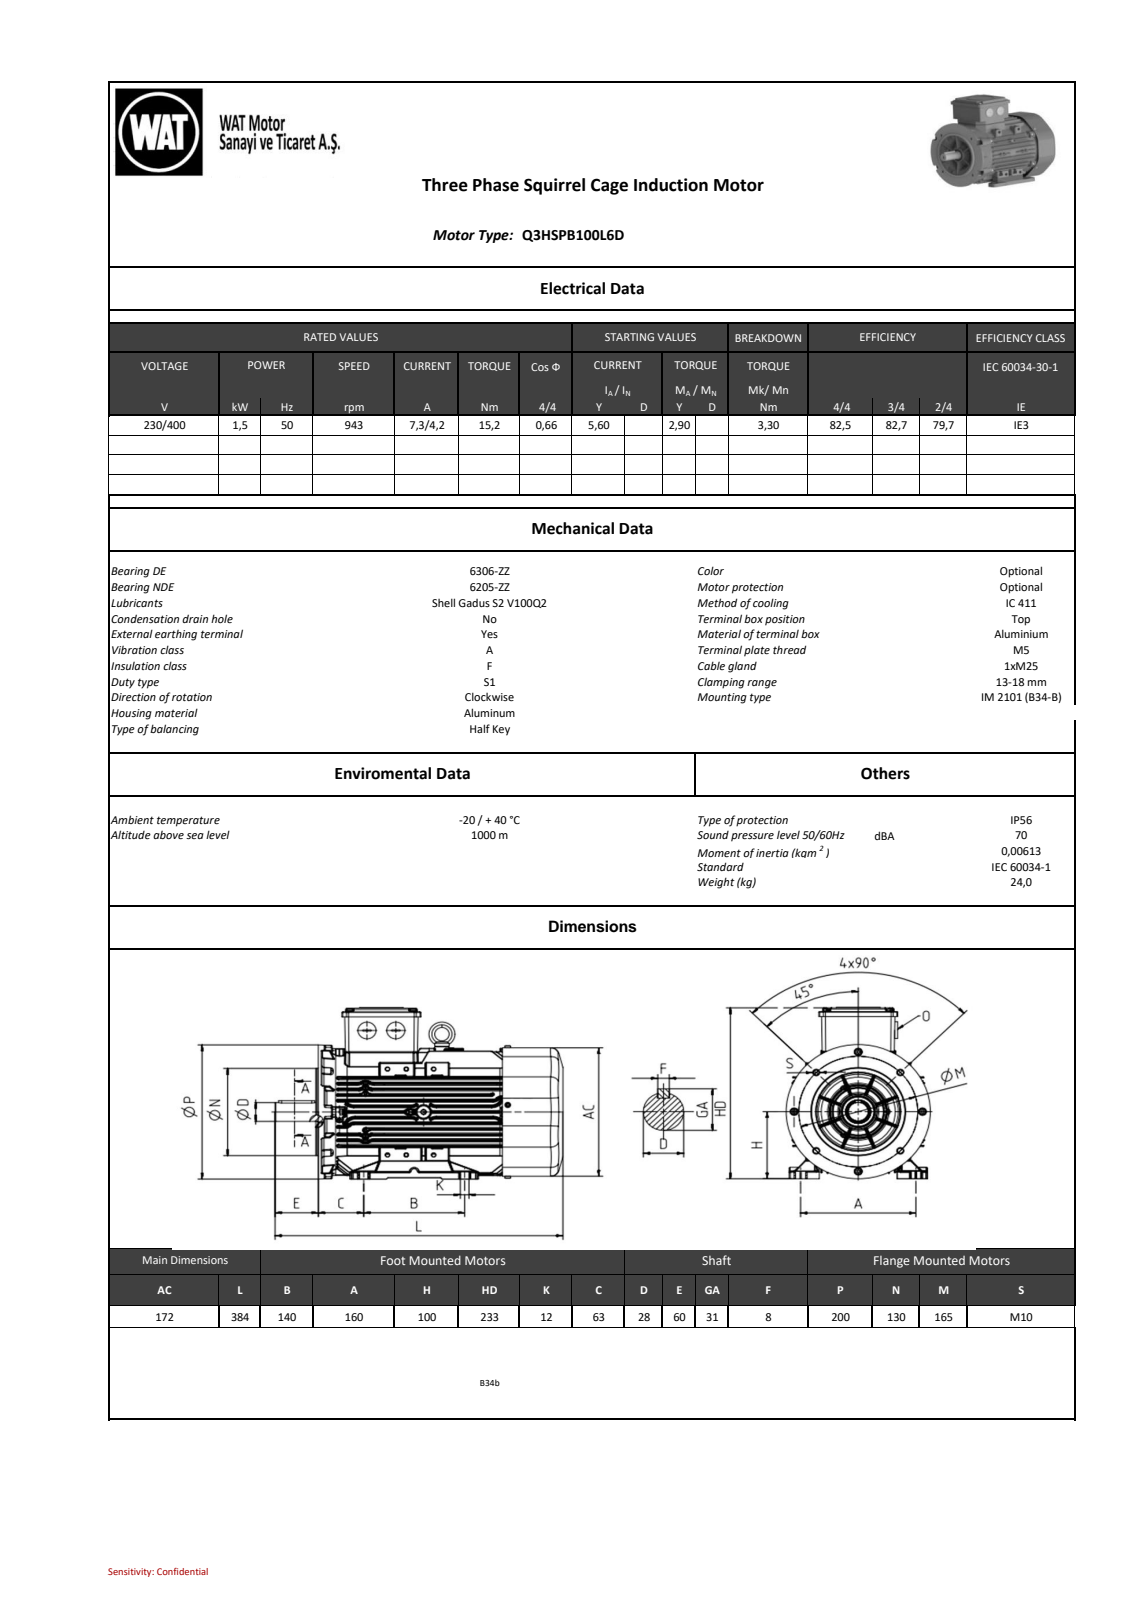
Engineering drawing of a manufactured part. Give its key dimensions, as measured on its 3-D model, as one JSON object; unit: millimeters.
{"part_name": "QHS Series_ 100_B34b DEEP COVER_stp_objects", "step_written_by": "SIEMENS PLM Software NX2206.8101 (AUTOMOTIVE_DESIGN)", "units": "millimeters", "bodies": {"solids": 0, "faces": 7543, "planar": 1878, "cylindrical": 3298, "other": 2367}, "overall_size": [384.19, 233.22, 200.35], "round_holes": [[9, 4], [3.5, 3], [8.5, 1], [9.87, 1], [10.5, 1], [79.79, 1], [97.79, 1], [115.78, 1]], "round_bosses_or_shafts": [[8, 7], [5, 5], [10, 4], [9.5, 4], [25, 2], [130, 1], [102.19, 1], [84.19, 1]], "partial_cylinders_radius": [[1, 723], [0.8, 605], [0.5, 542], [2, 190], [0.7, 75], [8, 28], [4, 10], [0.8, 9]], "face_to_face_distances": [7.5, 91.91, 42.5, 8.93, 82.98, 23.57, 206, 7.37, 50.35, 90.35], "hole_center_spacings": [82.51, 116.68, 39, 67.56, 82.4, 82.61, 165.01, 38.91]}
